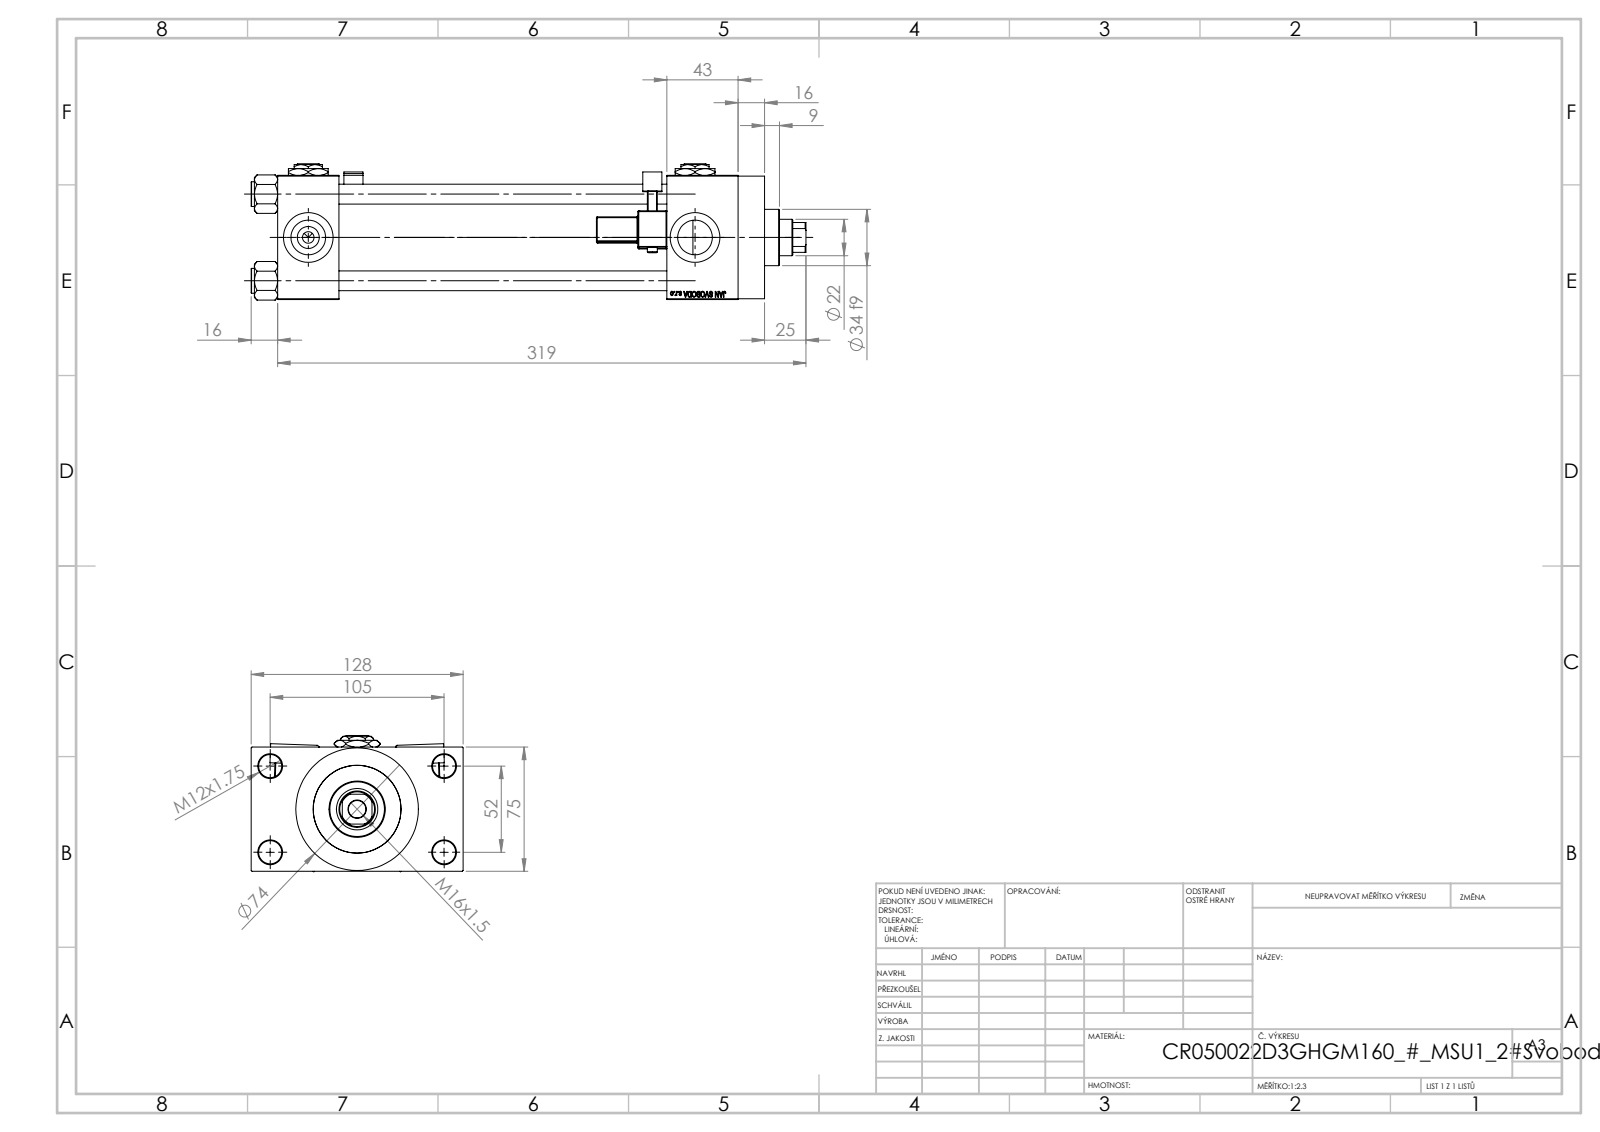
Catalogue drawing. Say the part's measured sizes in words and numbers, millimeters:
The part is named "Zatka_pro_OIL_PORT; V215CR_VCP_D; V215CR_D_TYCINKA; V215CR_MSU (+3 more)". Its 3-D file was written by "SolidWorks 2019 (CONFIG_CONTROL_DESIGN)". It is 15 solids with 1358 faces: 603 planar, 159 cylindrical and 596 other. Overall it measures 335 by 128 by 82.27 millimeters. Its volume is 1 021 000 cubic millimeters and its surface area 260 599 square millimeters. Round holes: 4 of diameter 12, 4 of diameter 14, 4 of diameter 20.96, 4 of diameter 30, 3 of diameter 7, 1 of diameter 10.5, 1 of diameter 22, 1 of diameter 25, 1 of diameter 41, 1 of diameter 50, 1 of diameter 53. Round bosses or shafts: 4 of diameter 15, 2 of diameter 6, 1 of diameter 74, 1 of diameter 56, 1 of diameter 34. Partial cylindrical surfaces (rounded edges, fillets, slot ends): 48 of radius 0.5, 2 of radius 1, 2 of radius 2.5, 2 of radius 4, 1 of radius 10.5. The main face-to-face distances are 75, 198, 37, 235, 26.5, 101.5, 278, 241, 43, 16. The hole center spacings are 26.35, 36.98, 52.3, 58.43, 58.59, 78.65, 94.37, 52.
